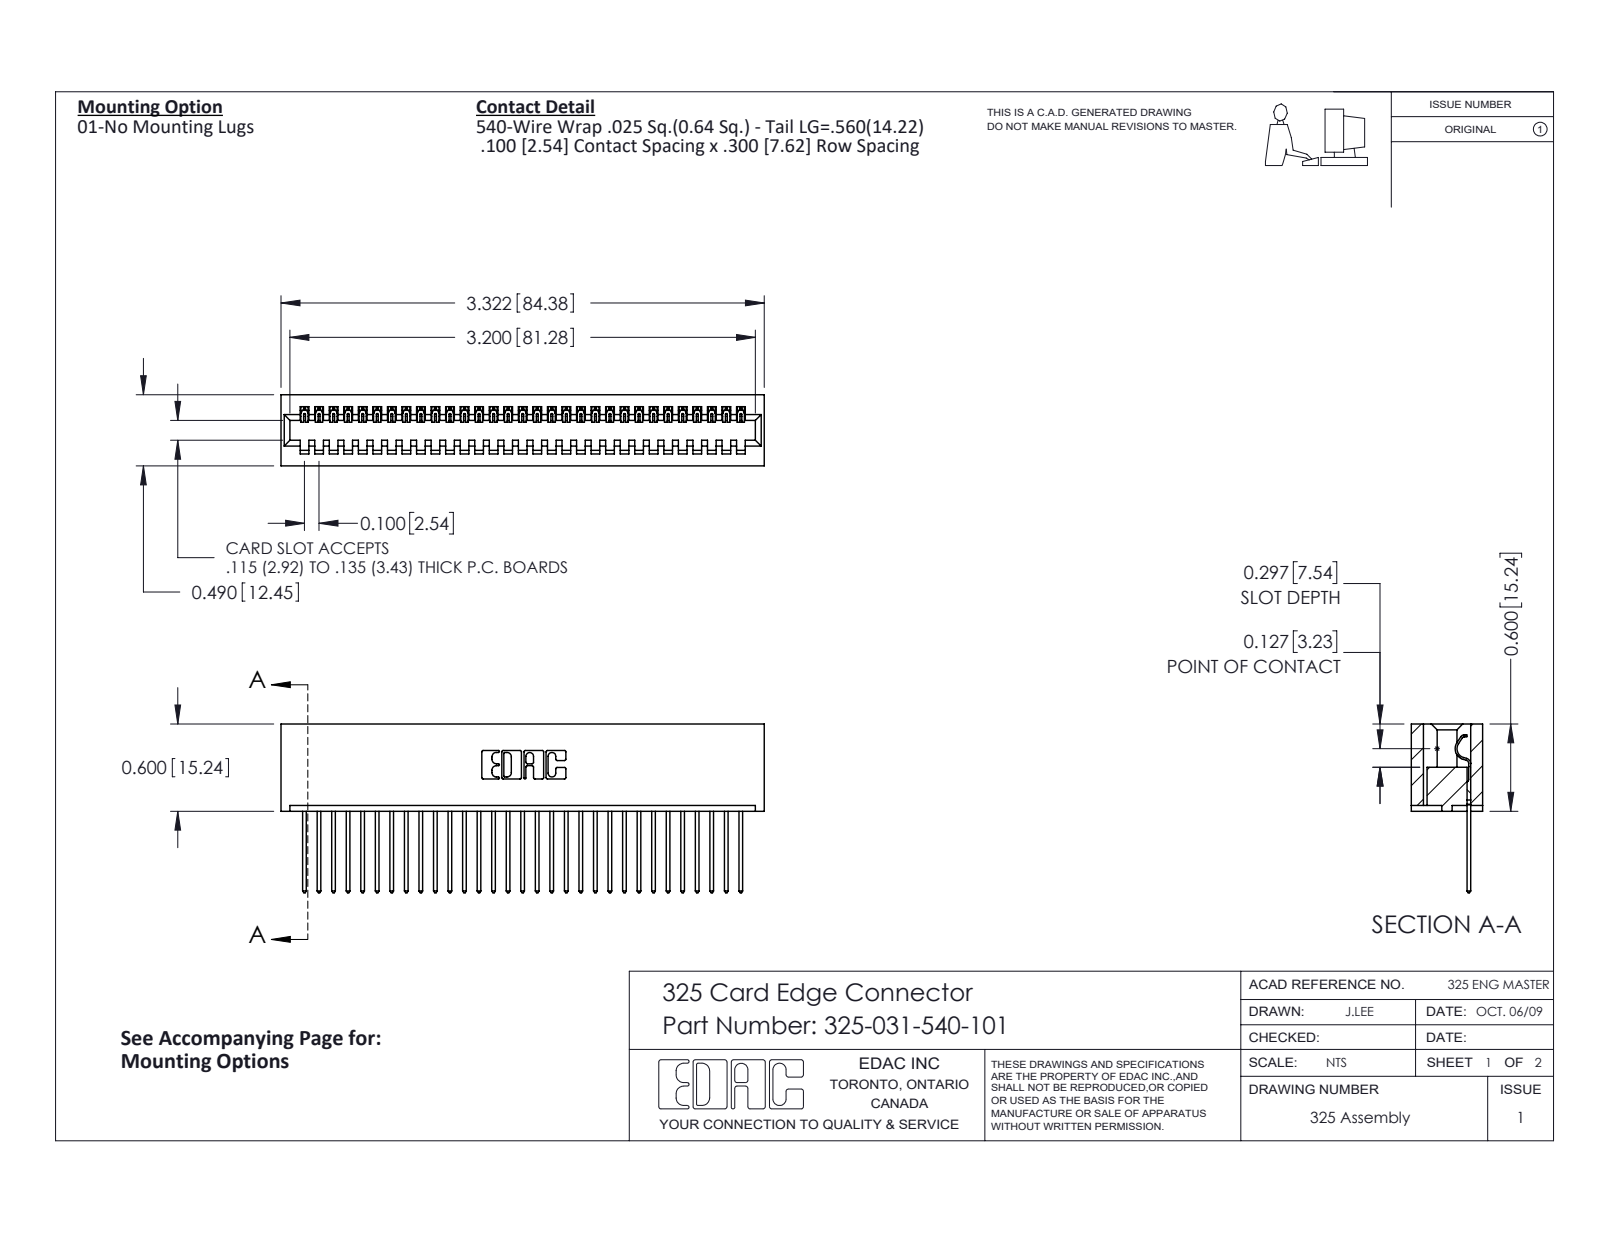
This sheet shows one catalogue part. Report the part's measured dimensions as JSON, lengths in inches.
{"part_name": "325 Part_Lugless; 325-292-001_325-293-140; 325-031-540-101", "step_written_by": "SolidWorks 2016 (CONFIG_CONTROL_DESIGN)", "units": "inches", "bodies": {"solids": 32, "faces": 1904, "planar": 1368, "cylindrical": 536, "other": 0}, "overall_size": [3.322, 1.16, 0.49], "volume_in3": 0.686, "surface_area_in2": 19.98, "partial_cylinders_radius": [[0.006, 62], [0.01, 62], [0.01, 22], [0.007, 6], [0.031, 6], [0.026, 3], [0.014, 1], [0.022, 1]], "face_to_face_distances": [0.083, 0.407, 0.3, 0.49, 0.107, 0.383, 0.025, 0.325, 0.1, 0.2]}
